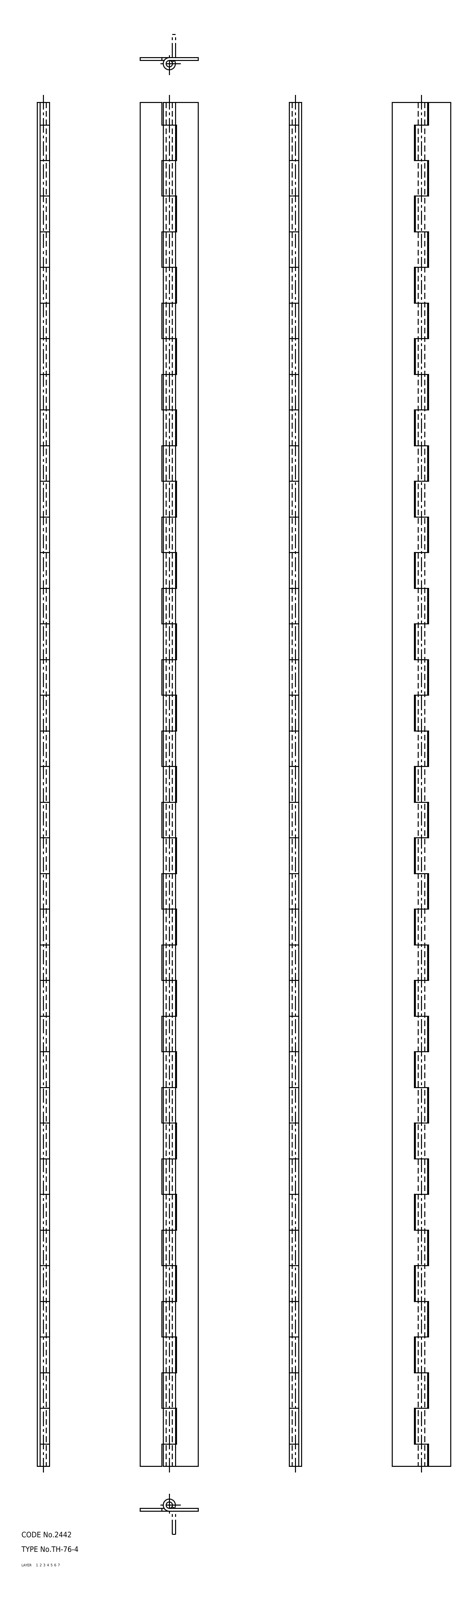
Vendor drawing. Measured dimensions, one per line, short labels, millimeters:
name: hinge piece_B; hinge piece_A; shaft; TH_76_4
written by: SolidWorks 2015 (AUTOMOTIVE_DESIGN)
unit: mm
bodies: 3 solids, 246 faces (166 planar, 80 cylindrical, 0 other)
size: 750 × 32 × 6.7
volume: 56 812 mm³; area: 77 300 mm²
holes: 1× ⌀3.5
bosses: 1× ⌀6.7
face distances: 1.6, 32, 12, 20, 39.2, 78.4, 117.6, 156.8, 196, 8
